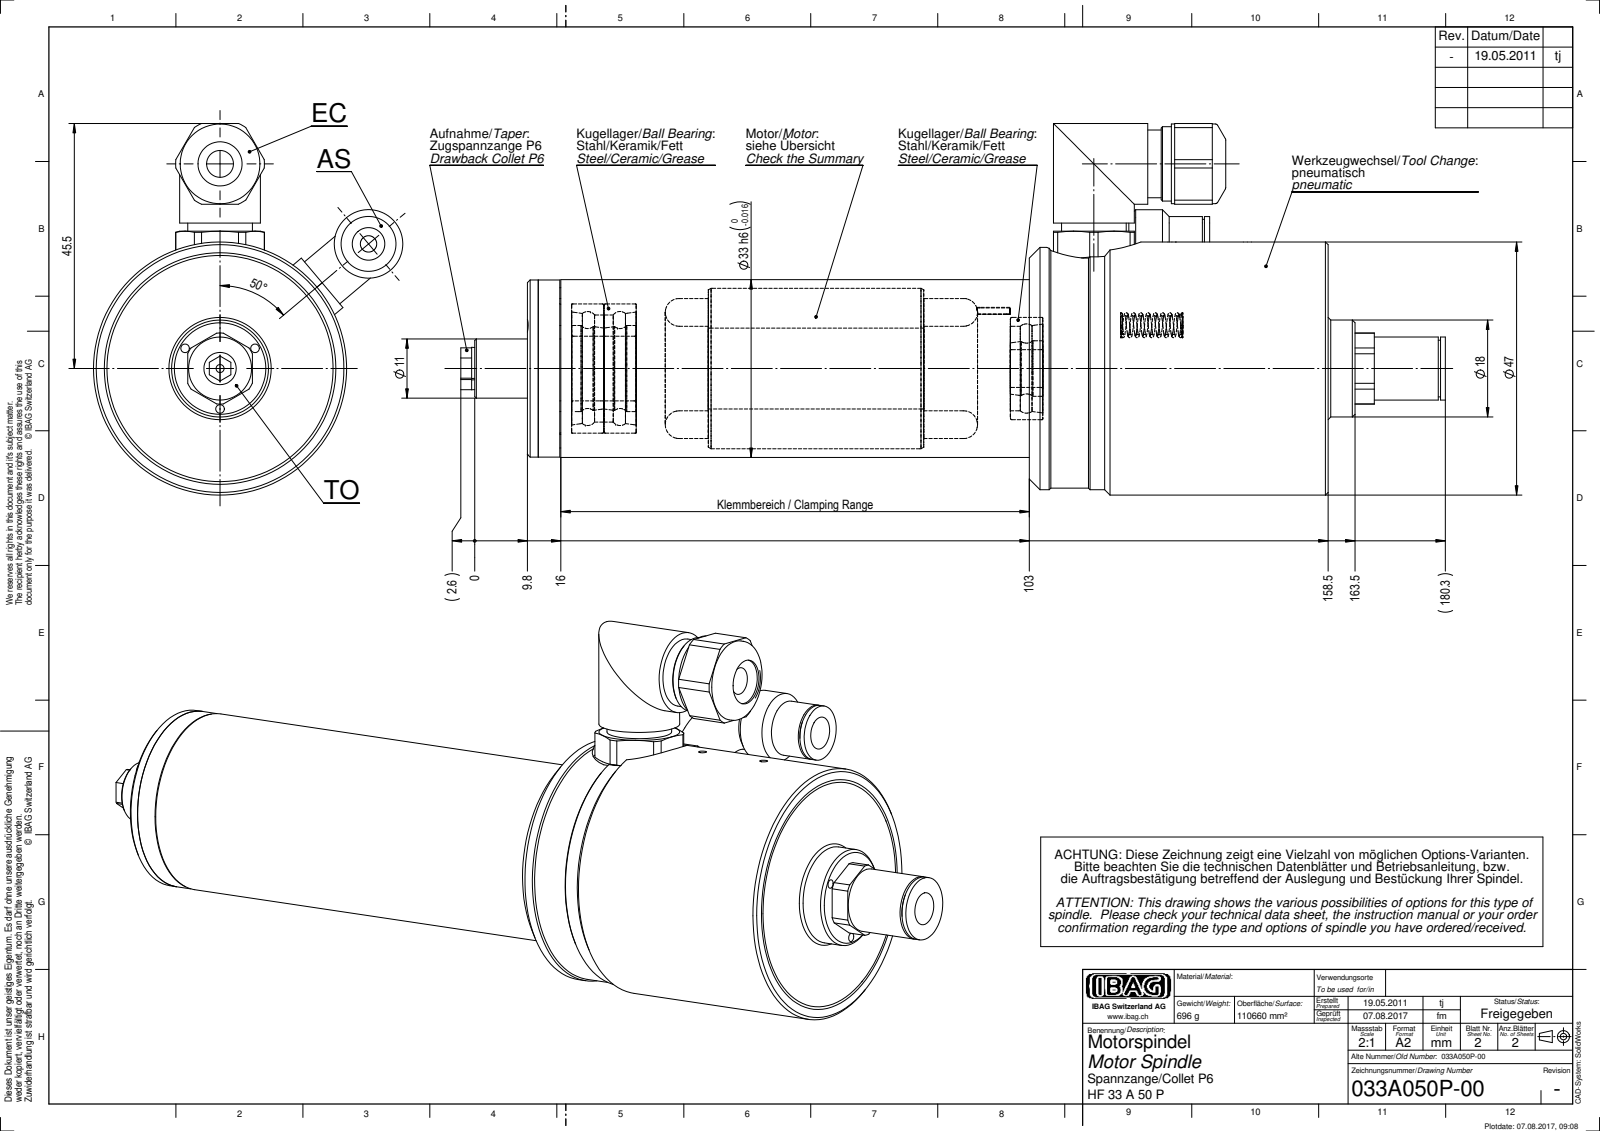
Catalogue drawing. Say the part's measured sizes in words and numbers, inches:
The part is named "033A050P-00". Its 3-D file was written by "SolidWorks 2010 (CONFIG_CONTROL_DESIGN)". It is 0 solids with 276 faces: 89 planar, 122 cylindrical and 65 other. Overall it measures 7.199 by 2.717 by 2.261 inches. Round holes: 3 of diameter 0.063, 2 of diameter 0.059, 2 of diameter 0.236, 1 of diameter 0.079, 1 of diameter 0.197, 1 of diameter 0.323, 1 of diameter 0.449, 1 of diameter 0.591, 1 of diameter 0.689. Round bosses or shafts: 3 of diameter 0.197, 2 of diameter 0.591, 2 of diameter 0.4, 1 of diameter 1.85, 1 of diameter 1.772, 1 of diameter 1.748, 1 of diameter 1.339, 1 of diameter 1.299. Partial cylindrical surfaces (rounded edges, fillets, slot ends): 3 of radius 0.03, 2 of radius 0.325, 1 of radius 0.26. The main face-to-face distances are 5.776, 0.079, 5.854, 3.669, 3.591, 2.185, 0.244, 0.165, 3.425, 5.61. The hole center spacings are 0.295, 0.511, 1.372, 0.512, 0.551, 0.571, 1.122, 1.128.
